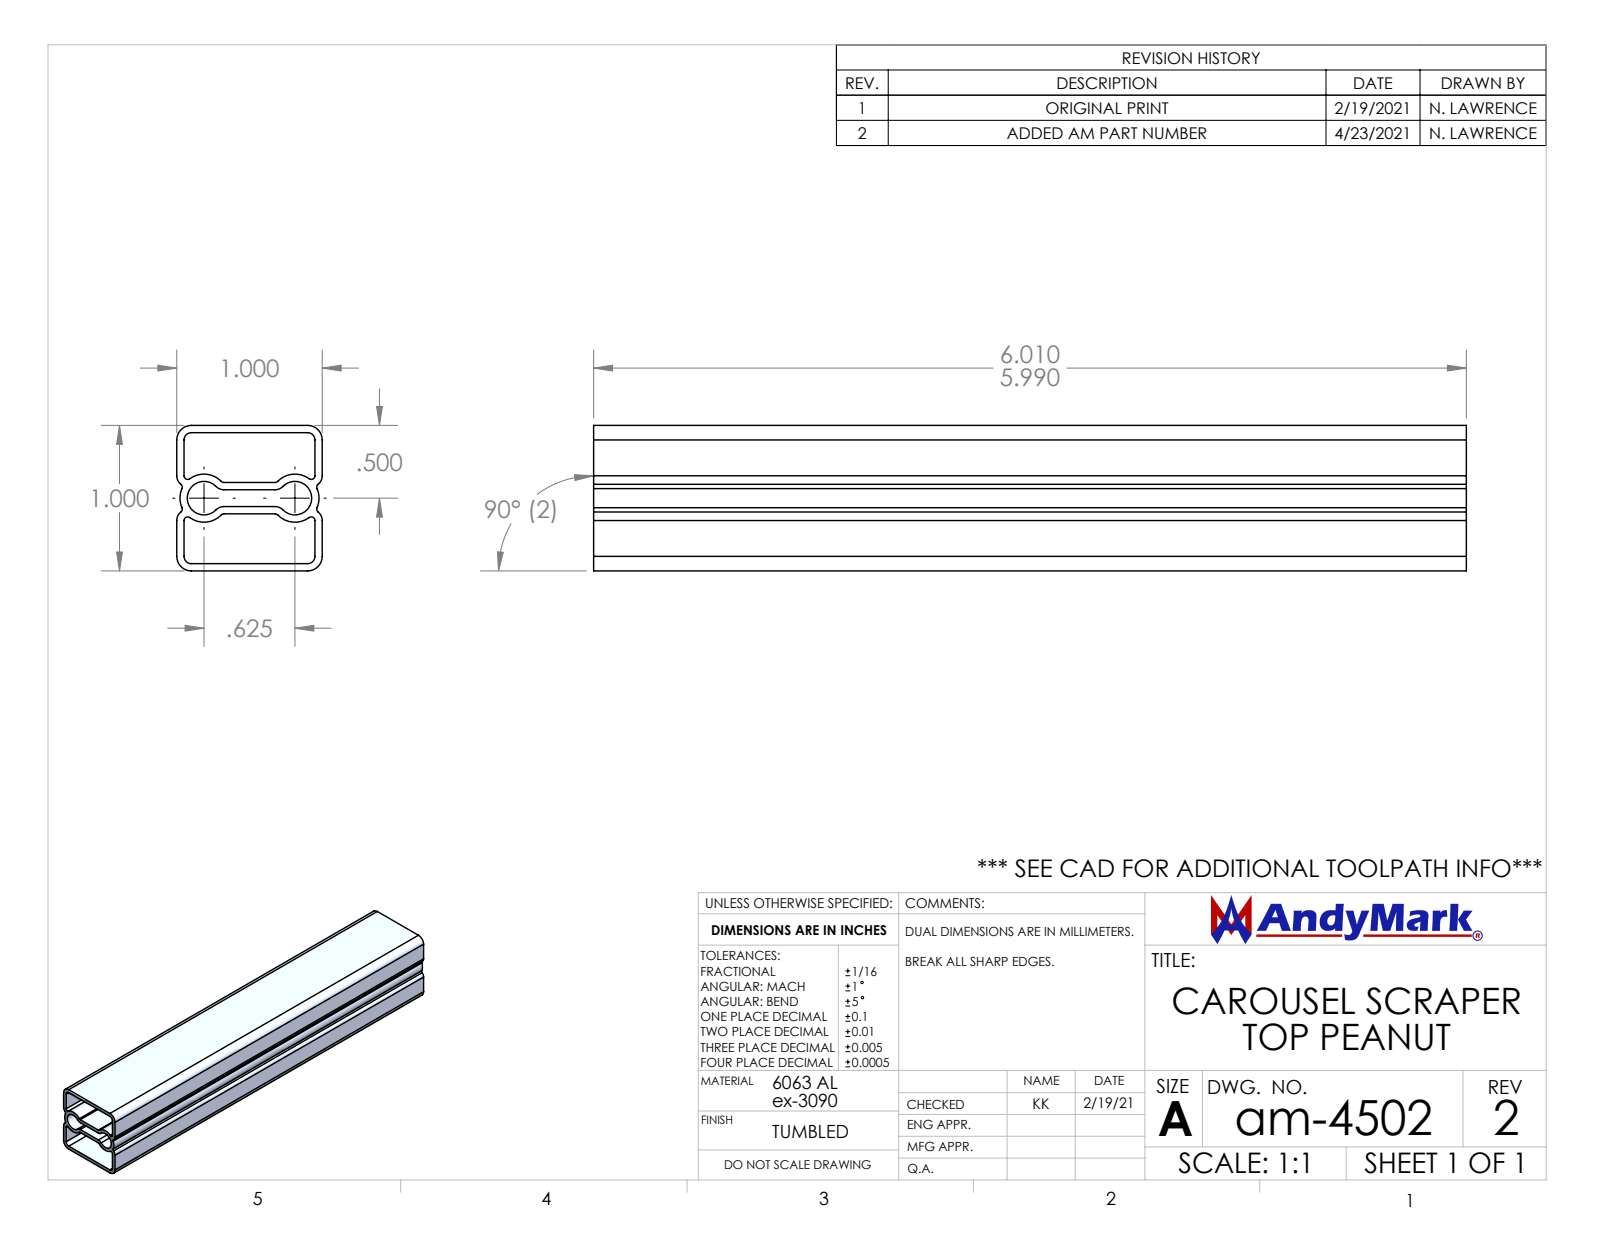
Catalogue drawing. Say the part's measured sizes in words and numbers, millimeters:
The part is named "am-4502 Carousel Scraper Top Peanut". Its 3-D file was written by "SolidWorks 2019 (AUTOMOTIVE_DESIGN)". It is 1 solid with 54 faces: 18 planar, 36 cylindrical and 0 other. Overall it measures 152.4 by 25.4 by 25.4 millimeters. Its volume is 27 140 cubic millimeters and its surface area 42 060 square millimeters. Partial cylindrical surfaces (rounded edges, fillets, slot ends): 12 of radius 0.6, 8 of radius 1.9, 4 of radius 1.3, 4 of radius 2.5, 2 of radius 2.9, 2 of radius 4.2. The main face-to-face distances are 1.3, 24.1, 10, 14.2, 22.9, 25.4, 11.2, 15.4, 8.7, 12.9.
